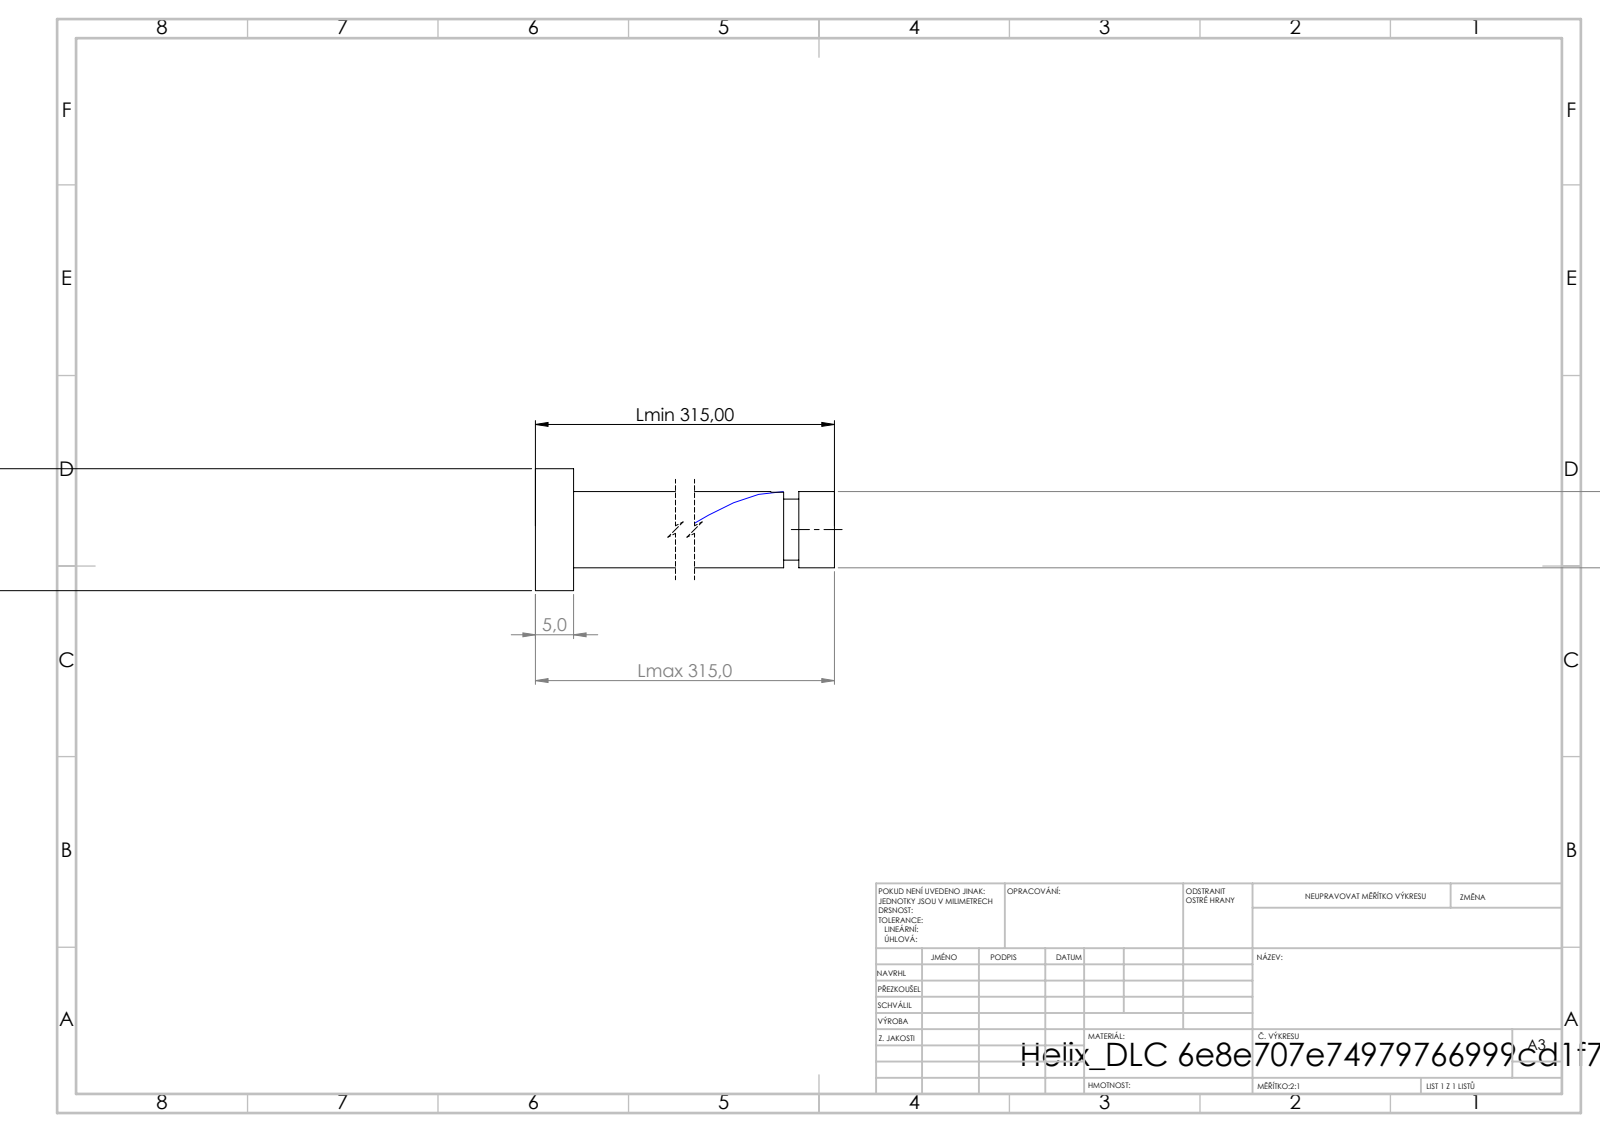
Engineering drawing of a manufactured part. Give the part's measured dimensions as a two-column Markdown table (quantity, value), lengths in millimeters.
| quantity | value |
| --- | --- |
| STEP written by | SolidWorks 2019 (CONFIG_CONTROL_DESIGN) |
| units | millimeters |
| bodies | 1 solid, 21 faces (6 planar, 14 cylindrical, 1 other) |
| overall size | 315 × 16 × 16 |
| volume | 25 059 mm³ |
| surface area | 10 621 mm² |
| round bosses / shafts (diameter × count) | 16 × 1, 10 × 1, 8 × 1 |
| main face-to-face distances | 5, 315, 310, 310.33, 305.33, 4.67, 308.33, 303.33, 2, 6.67 |
